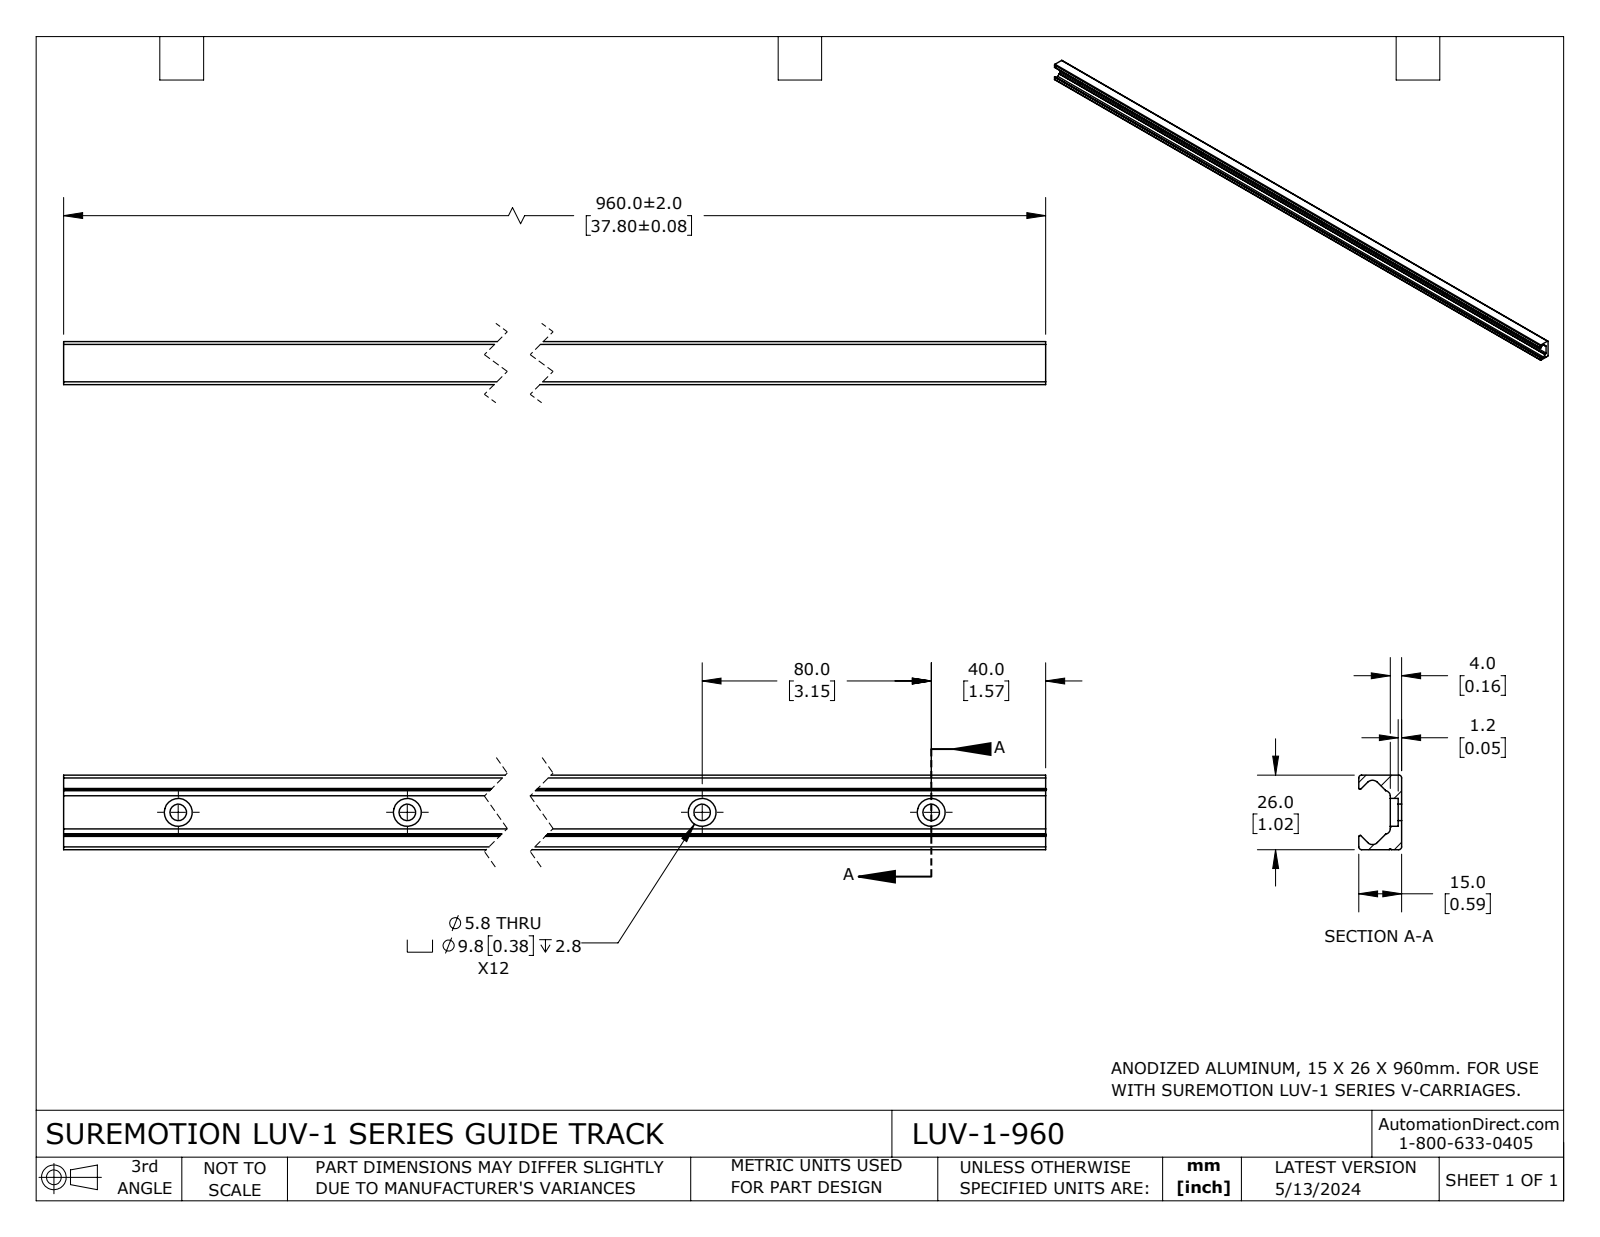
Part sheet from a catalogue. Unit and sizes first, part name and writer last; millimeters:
Units: millimetres
Overall size (bounding box): 960 × 26.01 × 15.01
Round holes (diameter × count): ⌀5.79 ×12, ⌀9.75 ×12
Partial cylindrical surfaces — rounded edges, fillets, slot ends (radius × count): R0.99 ×4, R0.51 ×2, R0.64 ×2, R0.76 ×2, R1.78 ×2, R2.39 ×2, R0.33 ×1
Main face-to-face distances: 26.02, 4.01, 15.02, 11.01, 17.27, 1.21, 2.8, 13.81, 960
Hole centre spacings: 80, 160, 240, 320, 400, 480, 560, 640
Volume: 172 858 mm³ · Surface area: 101 920 mm²
Bodies: 1 solid, 88 faces (25 planar, 63 cylindrical, 0 other)
Part name (STEP PRODUCT): LUV-1-960
STEP written by: SolidWorks 2023 (CONFIG_CONTROL_DESIGN)
